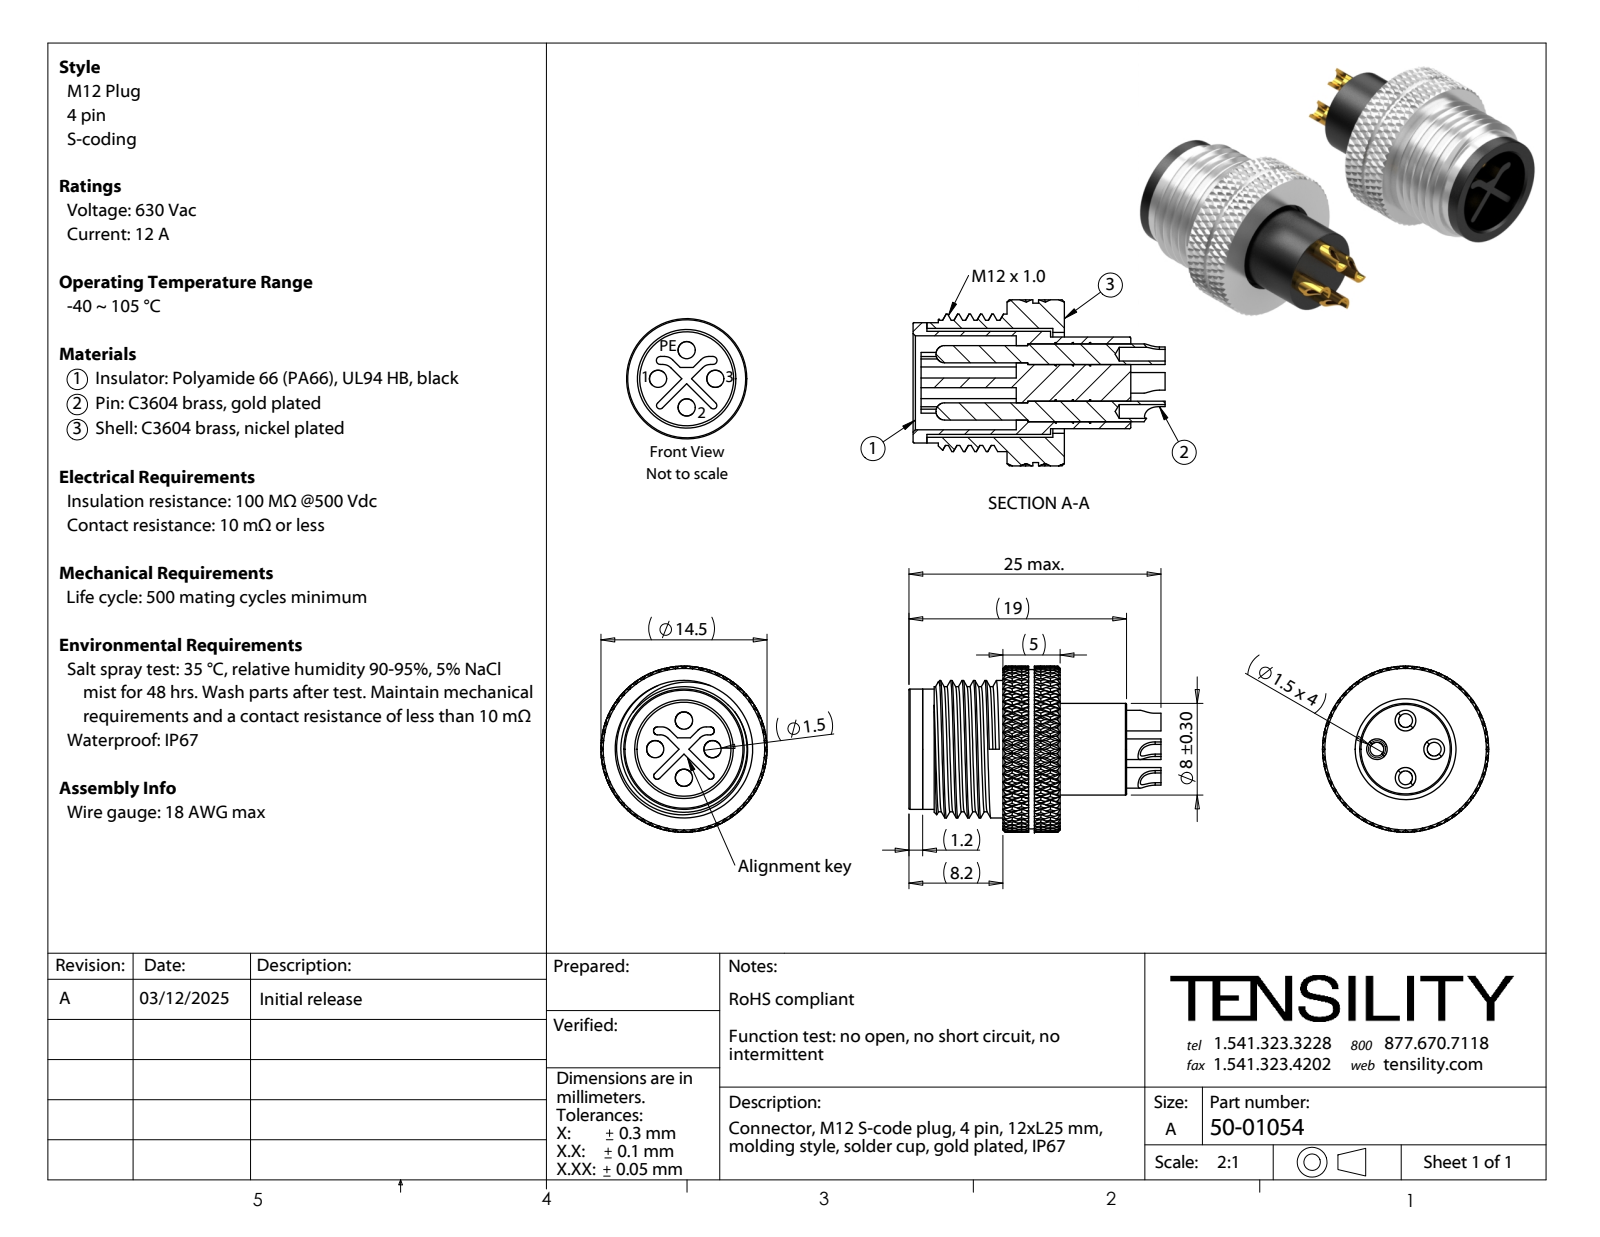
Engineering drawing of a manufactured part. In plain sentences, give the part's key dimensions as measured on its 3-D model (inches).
The part is named "50-01054-02_step; 50-01054-03L; 50-01054-03; 50-01054 (+1 more)". Its 3-D file was written by "SolidWorks 2021 (CONFIG_CONTROL_DESIGN)". It is 6 solids with 232 faces: 59 planar, 109 cylindrical and 64 other. Overall it measures 0.866 by 0.571 by 0.571 inches. Its volume is 0.09 cubic inches and its surface area 4.627 square inches. Round holes: 4 of diameter 0.047, 4 of diameter 0.059, 1 of diameter 0.323, 1 of diameter 0.346, 1 of diameter 0.374. Round bosses or shafts: 4 of diameter 0.071, 1 of diameter 0.571, 1 of diameter 0.547, 1 of diameter 0.472, 1 of diameter 0.413, 1 of diameter 0.354, 1 of diameter 0.315. Partial cylindrical surfaces (rounded edges, fillets, slot ends): 4 of radius 0.039, 2 of radius 0.012, 2 of radius 0.014, 2 of radius 0.067. The main face-to-face distances are 0.024, 0.472, 0.394, 0.276, 0.425, 0.197, 0.307, 0.228, 0.031, 0.047. The hole center spacings are 0.098, 0.139, 0.197.
